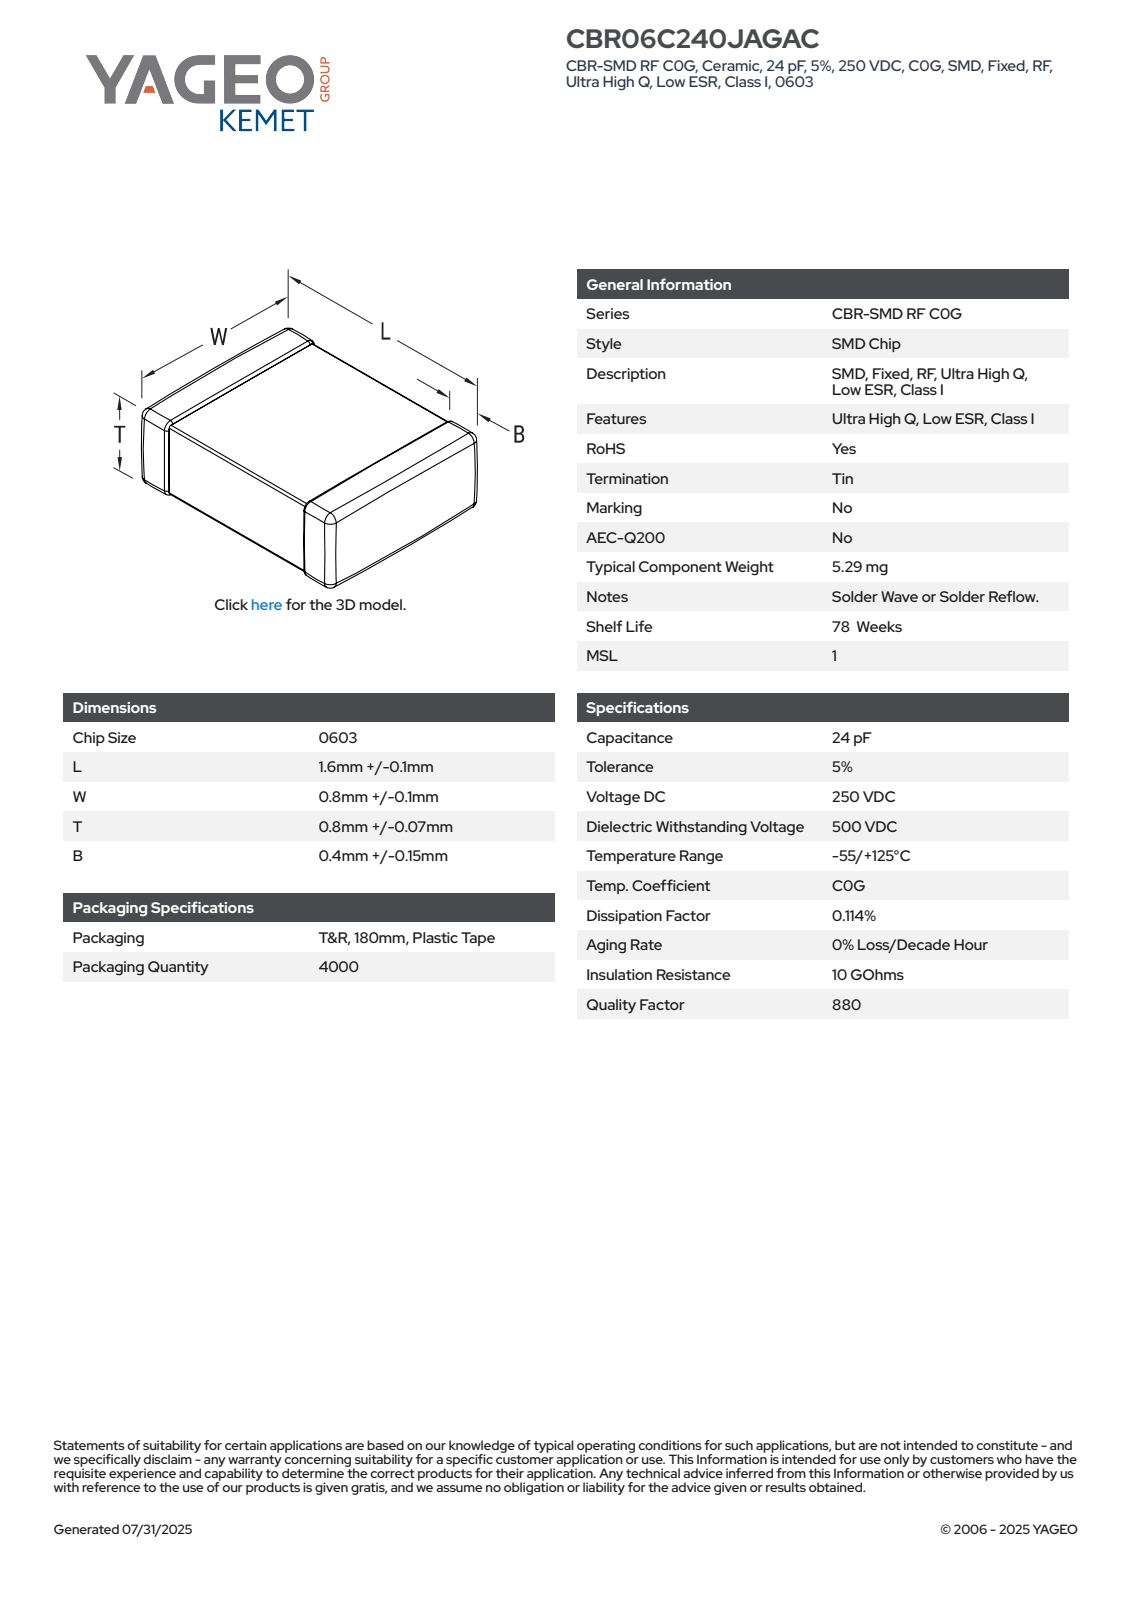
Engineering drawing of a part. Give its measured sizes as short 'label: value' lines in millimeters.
name: CCS_CCSTDNOS_0603_L1.7W0.9T0.87B0.55
written by: SolidWorks 2014 (AUTOMOTIVE_DESIGN)
unit: mm
bodies: 4 solids, 125 faces (71 planar, 38 cylindrical, 16 other)
size: 1.7 × 0.9 × 0.87
volume: 1 mm³; area: 8 mm²
face distances: 0.85, 0.88, 0.87, 0.9, 1.7, 0.86, 0.83, 0.84, 0.38, 0.5
